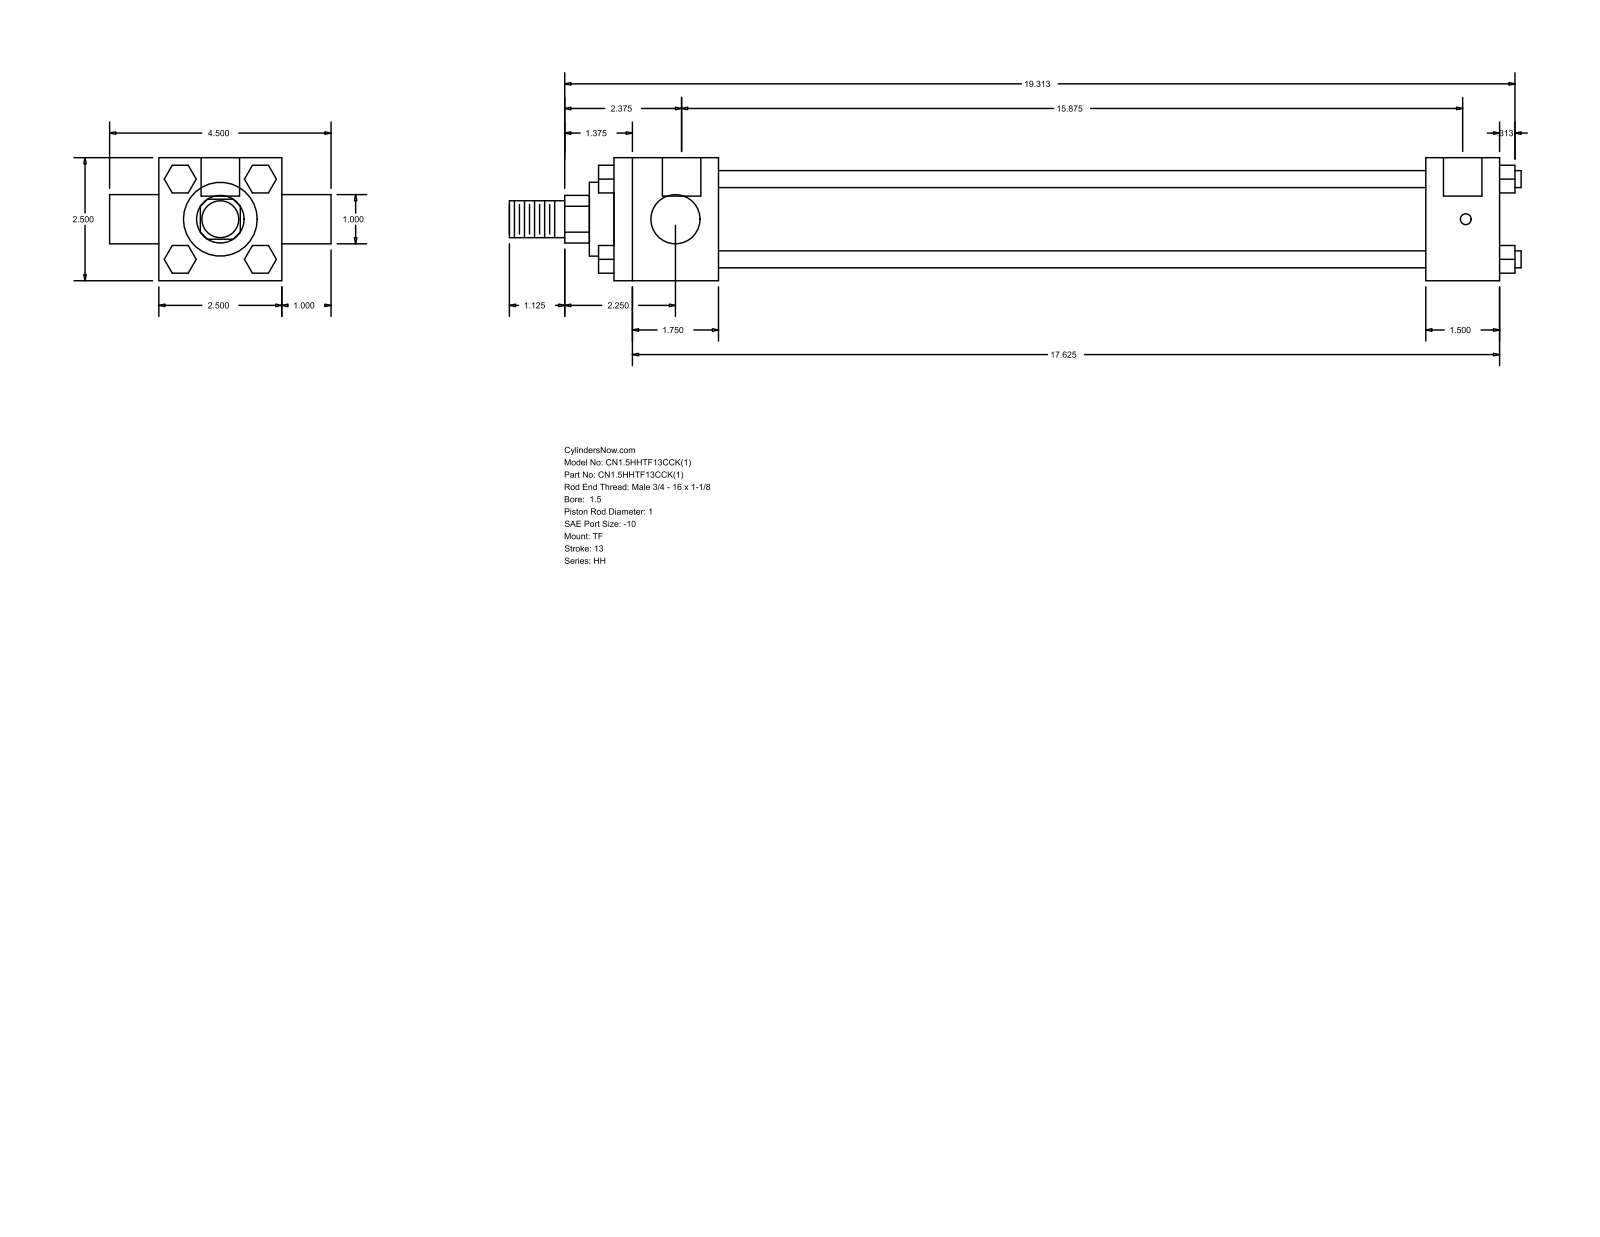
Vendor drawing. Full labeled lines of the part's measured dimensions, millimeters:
Part name (STEP PRODUCT): HH_TF__0150_1
STEP written by: GSSL Pune (CONFIG_CONTROL_DESIGN)
Units: millimetres
Bodies: 0 solids, 120 faces (92 planar, 28 cylindrical, 0 other)
Overall size (bounding box): 522.29 × 114.3 × 63.5
Round holes (diameter × count): ⌀5.56 ×3, ⌀19.84 ×2
Round bosses / shafts (diameter × count): ⌀8.76 ×4, ⌀25.4 ×2, ⌀44.45 ×1, ⌀38.1 ×1, ⌀19.05 ×1
Partial cylindrical surfaces — rounded edges, fillets, slot ends (radius × count): R12.29 ×1
Main face-to-face distances: 63.5, 38.1, 403.22, 365.12, 53.98, 419.1, 457.2, 25.4, 20.7, 14.29
Hole centre spacings: 1.59, 404.81, 403.22, 406.4
